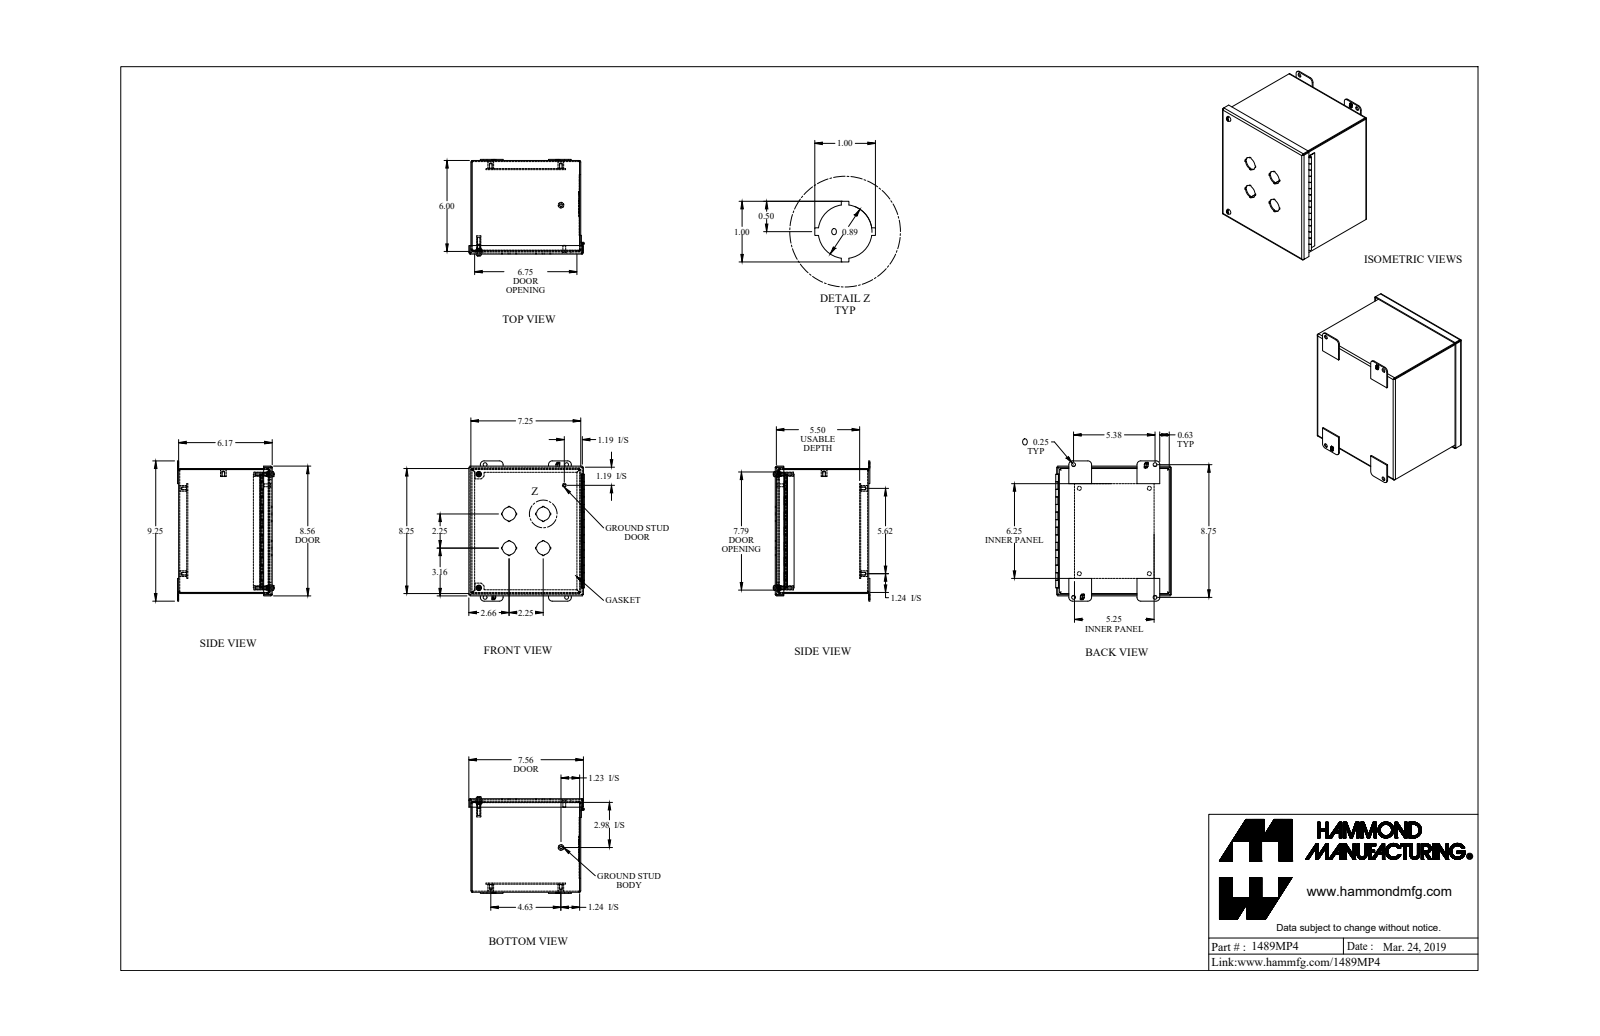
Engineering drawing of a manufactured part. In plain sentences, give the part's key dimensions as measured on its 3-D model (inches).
The part is named "1489MP4_Default". Its 3-D file was written by "SolidWorks 2019 (CONFIG_CONTROL_DESIGN)". It is 21 solids with 726 faces: 484 planar, 176 cylindrical and 66 other. Overall it measures 9.25 by 7.623 by 6.371 inches. Its volume is 30.82 cubic inches and its surface area 822 square inches. Round holes: 6 of diameter 0.25, 5 of diameter 0.156, 4 of diameter 0.265, 4 of diameter 0.886, 2 of diameter 0.159, 2 of diameter 0.406. Round bosses or shafts: 5 of diameter 0.375, 2 of diameter 0.39, 2 of diameter 0.275, 2 of diameter 0.19, 2 of diameter 0.148, 1 of diameter 0.25, 1 of diameter 0.188, 1 of diameter 0.174. Partial cylindrical surfaces (rounded edges, fillets, slot ends): 12 of radius 0.036, 12 of radius 0.108, 8 of radius 0.25, 2 of radius 0.125, 2 of radius 0.16, 2 of radius 0.171. The main face-to-face distances are 0.072, 6.1, 7.178, 0.072, 8.178, 6.172, 5.568, 0.532, 6.028, 7.25. The hole center spacings are 4.625, 7.5, 1.607, 1.607, 2.25, 5.238, 5.239, 5.536.
